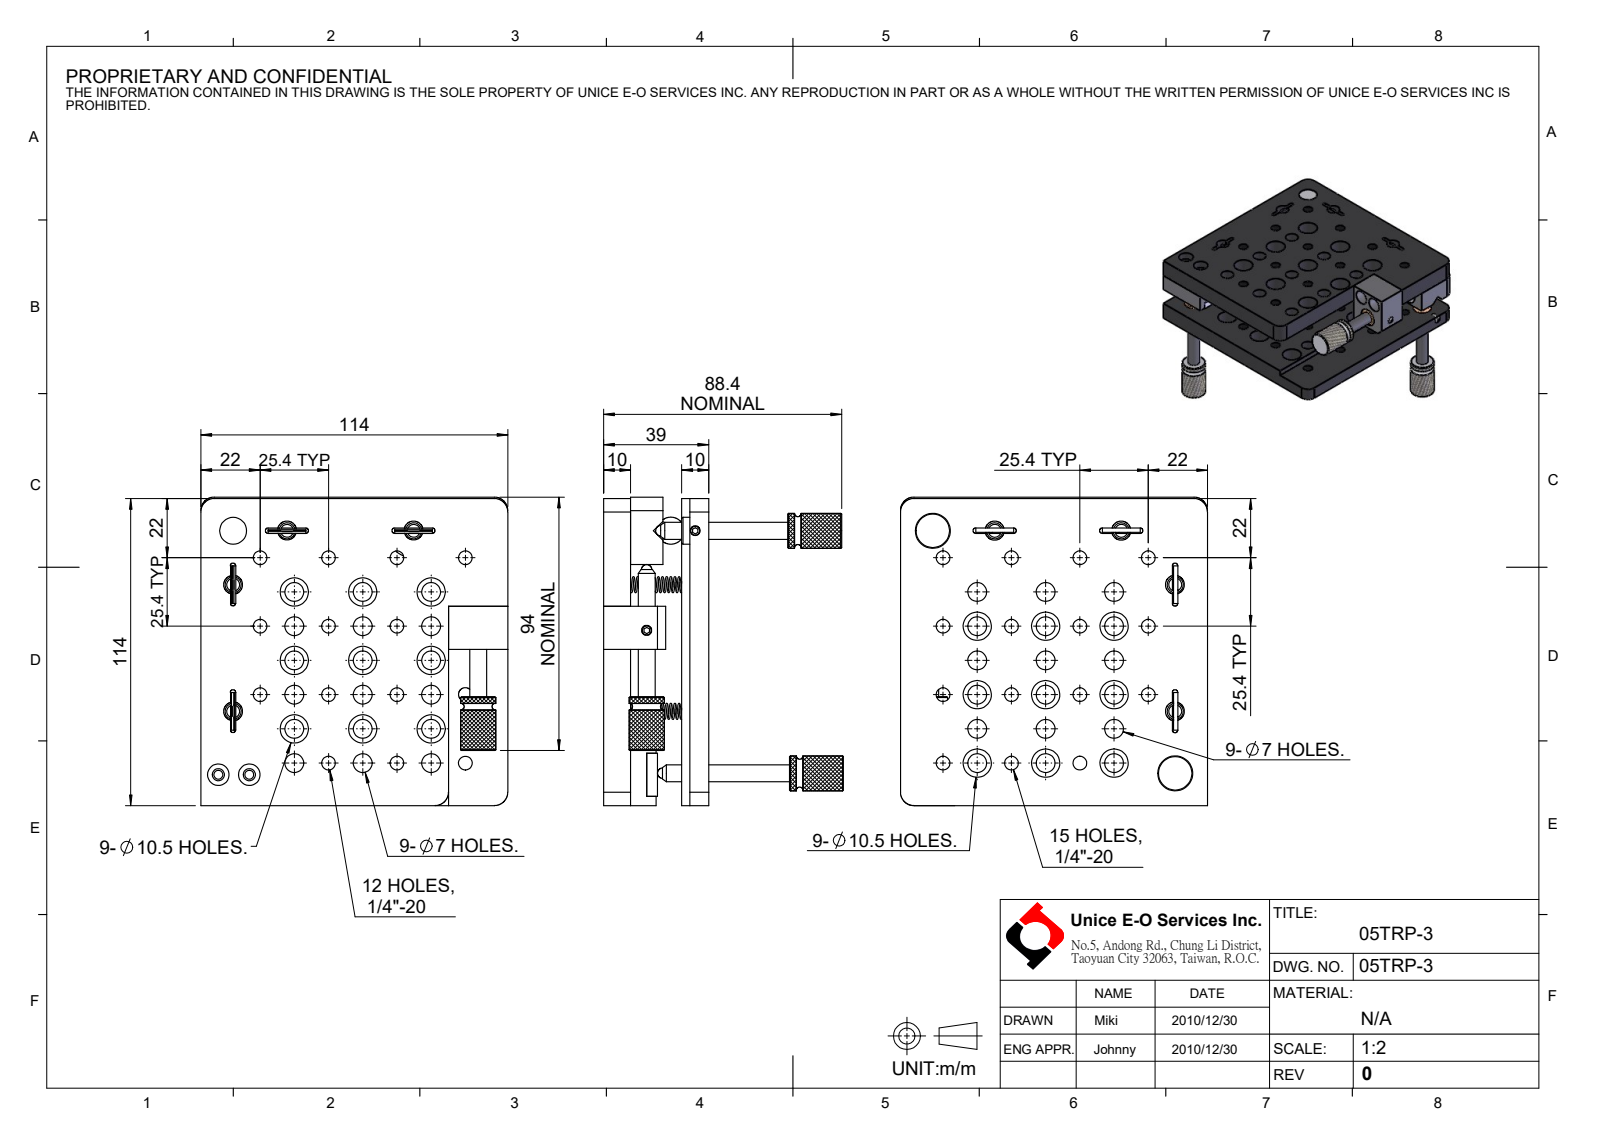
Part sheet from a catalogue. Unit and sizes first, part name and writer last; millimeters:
Units: millimetres
Overall size (bounding box): 114.5 × 114 × 89.03
Round holes (diameter × count): ⌀7 ×23, ⌀10.5 ×18, ⌀5.11 ×15, ⌀3.3 ×7, ⌀10 ×5, ⌀1.2 ×4, ⌀4.5 ×4, ⌀8 ×4, ⌀4 ×3, ⌀6.35 ×3, ⌀1.7 ×1, ⌀2.5 ×1
Round bosses / shafts (diameter × count): ⌀1.6 ×4, ⌀0.6 ×4, ⌀13 ×3, ⌀6.3 ×3, ⌀4 ×3
Partial cylindrical surfaces — rounded edges, fillets, slot ends (radius × count): R1 ×8, R5 ×6
Main face-to-face distances: 10, 29, 39, 19, 22, 7, 114, 12, 16, 3
Hole centre spacings: 28.4, 25.4, 40.16, 17.96, 56.8, 12.7, 35.92, 45.79
Volume: 257 840 mm³ · Surface area: 98 289 mm²
Bodies: 33 solids, 601 faces (186 planar, 290 cylindrical, 125 other)
Part name (STEP PRODUCT): 05TRP-3
STEP written by: SolidWorks 2016 (CONFIG_CONTROL_DESIGN)
